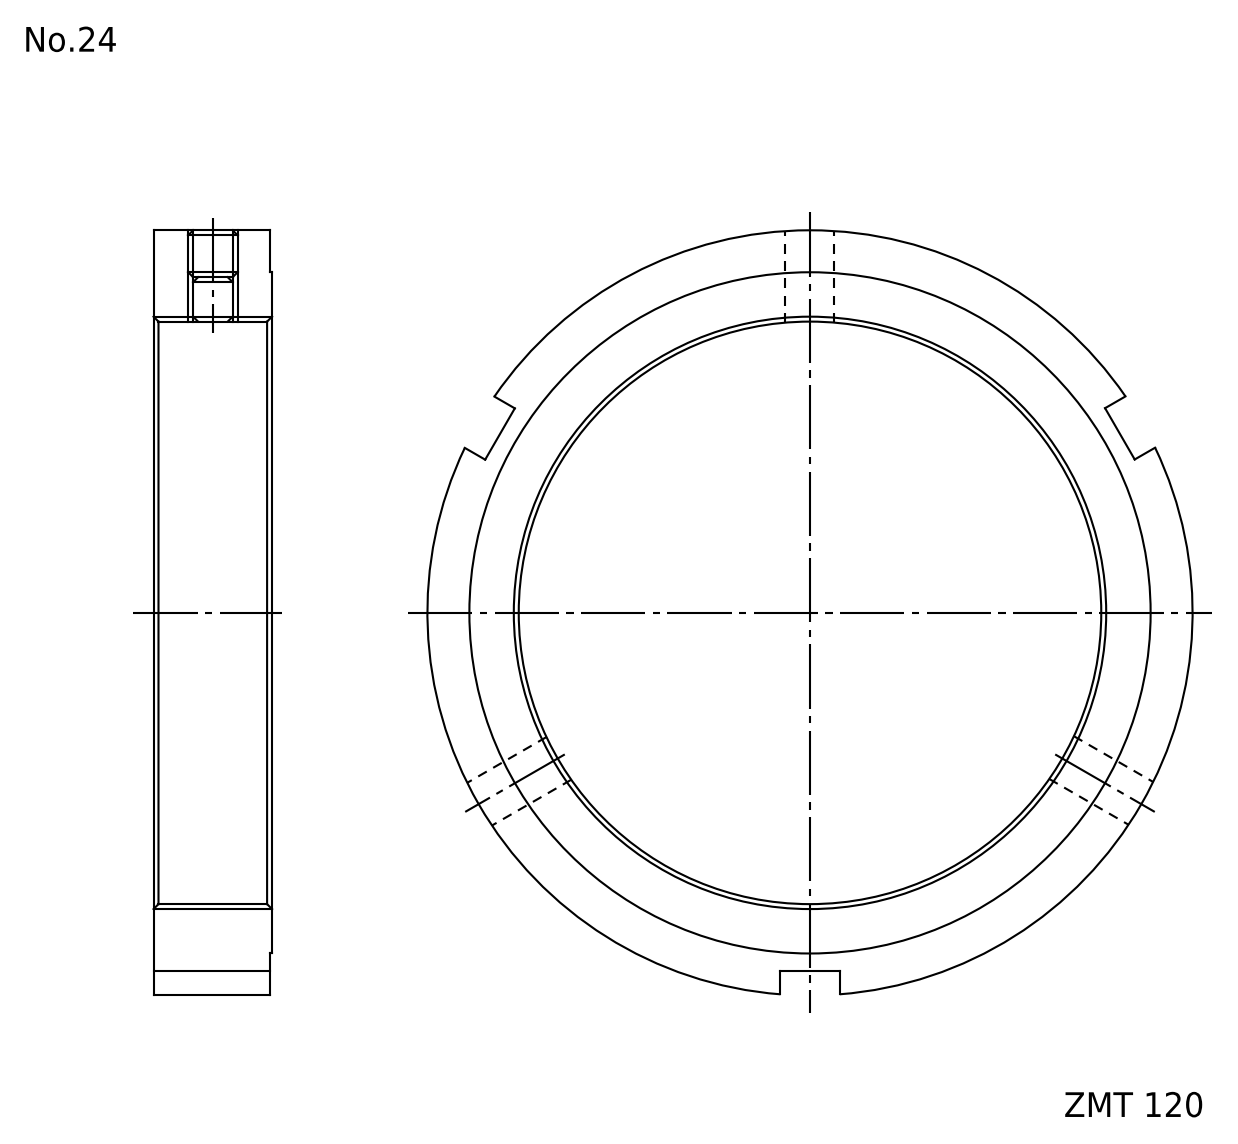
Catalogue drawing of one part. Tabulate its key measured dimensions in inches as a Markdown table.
| quantity | value |
| --- | --- |
| part name | FKD ZMT120 |
| STEP written by | Autodesk Inventor 2011 (AUTOMOTIVE_DESIGN) |
| units | inches |
| bodies | 1 solid, 20 faces (12 planar, 8 cylindrical, 0 other) |
| overall size | 6.102 × 6.093 × 0.945 |
| volume | 10.52 in³ |
| surface area | 57.65 in² |
| round holes (diameter × count) | 0.33 × 3, 4.724 × 1 |
| round bosses / shafts (diameter × count) | 6.102 × 1, 5.433 × 1 |
| main face-to-face distances | 0.925, 0.02, 0.945, 0.472 |
